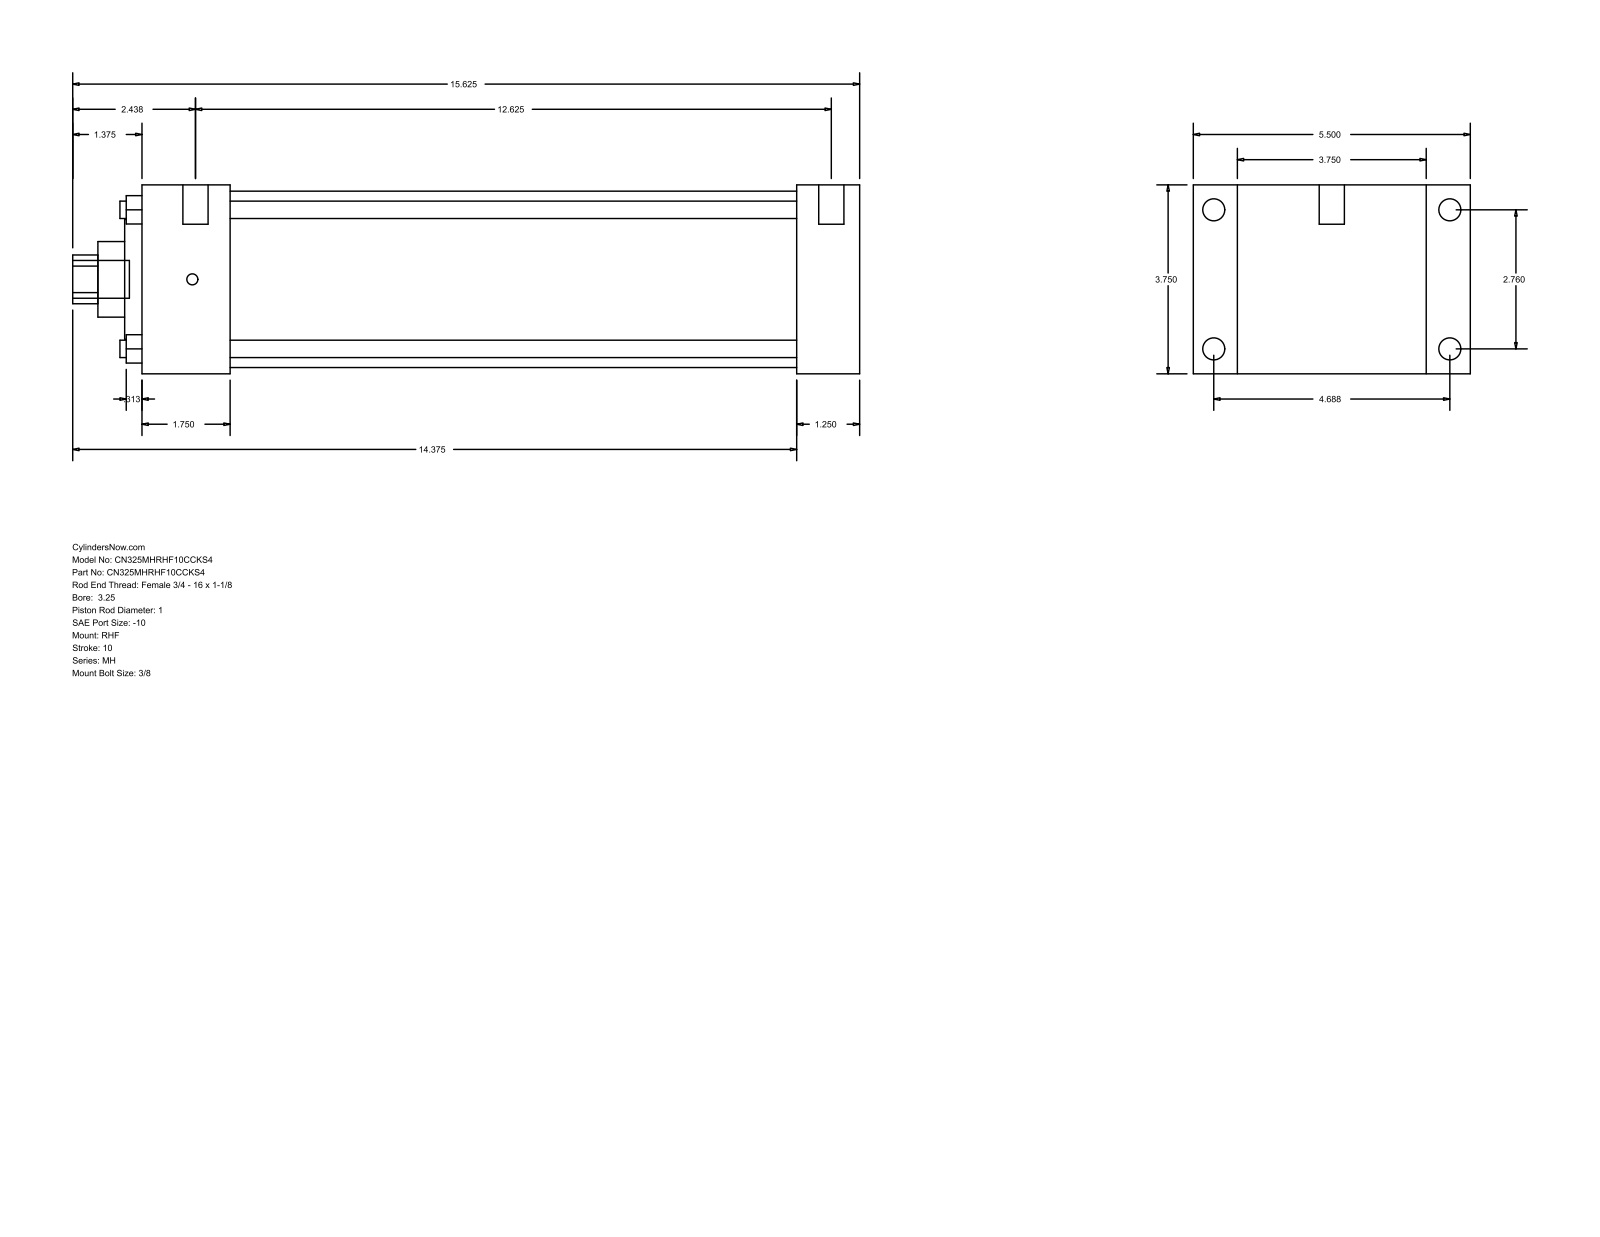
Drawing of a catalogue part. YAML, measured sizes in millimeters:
part_name: "MH_RHF__0325_1"
step_written_by: "GSSL Pune (CONFIG_CONTROL_DESIGN)"
units: millimeters
bodies: {solids: 0, faces: 90, planar: 61, cylindrical: 29, other: 0}
overall_size: [396.88, 139.7, 95.25]
round_holes:
  - {diameter: 8.76, count: 4}
  - {diameter: 25.4, count: 1}
  - {diameter: 38.1, count: 1}
  - {diameter: 60.33, count: 1}
  - {diameter: 88.9, count: 1}
round_bosses_or_shafts:
  - {diameter: 11.13, count: 4}
  - {diameter: 5.56, count: 4}
  - {diameter: 12.7, count: 2}
  - {diameter: 19.05, count: 1}
partial_cylinders:
  - {radius: 12.29, count: 1}
face_to_face_distances: [95.24, 31.76, 22.23, 117.47, 330.2, 361.96, 139.7, 44.46, 285.74, 317.5]
hole_center_spacings: [49.57, 70.1, 99.14]
